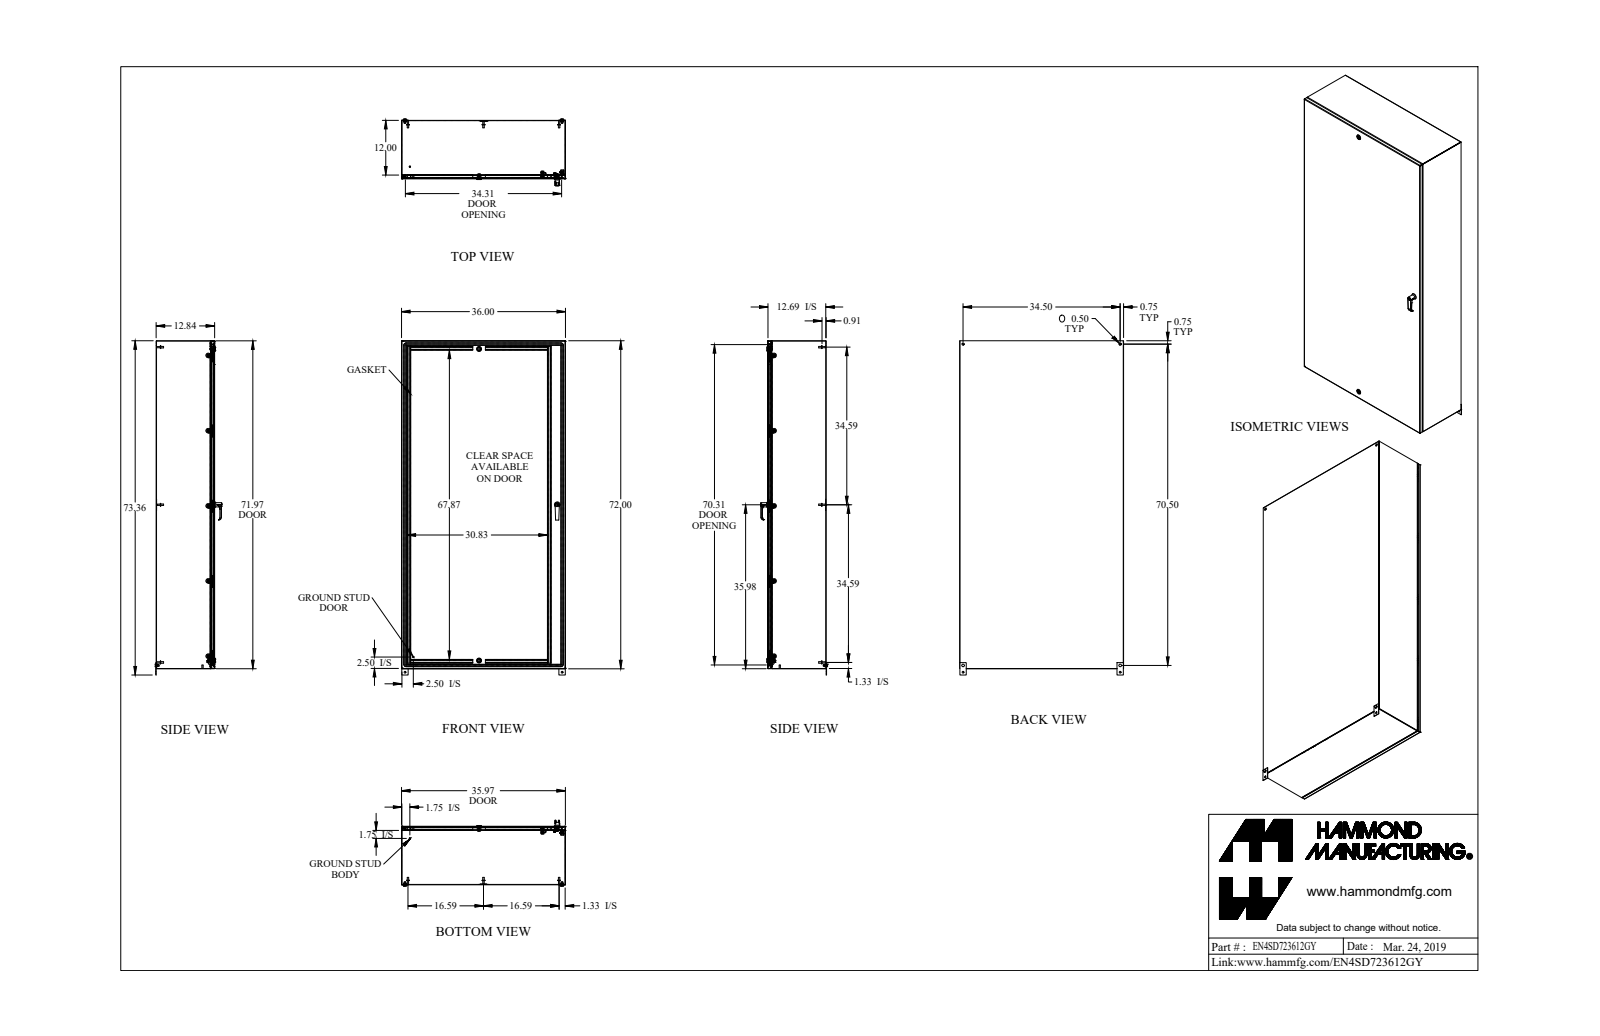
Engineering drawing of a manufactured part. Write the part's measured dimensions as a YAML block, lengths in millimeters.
part_name: "EN4SD723612GY"
step_written_by: "SolidWorks 2018 (AUTOMOTIVE_DESIGN)"
units: millimeters
bodies: {solids: 100, faces: 2461, planar: 1167, cylindrical: 902, other: 392}
overall_size: [1863.4, 914.4, 373.2]
volume: 10660000
surface_area: 11800000
round_holes:
  - {diameter: 4.5, count: 10}
  - {diameter: 5, count: 6}
  - {diameter: 6.4, count: 5}
  - {diameter: 6.7, count: 5}
  - {diameter: 10.5, count: 5}
  - {diameter: 6.5, count: 4}
  - {diameter: 8, count: 4}
  - {diameter: 9.9, count: 4}
  - {diameter: 10, count: 4}
  - {diameter: 12.7, count: 4}
  - {diameter: 5.9, count: 2}
  - {diameter: 7.8, count: 2}
round_bosses_or_shafts:
  - {diameter: 6.4, count: 11}
  - {diameter: 9.5, count: 10}
  - {diameter: 4, count: 10}
  - {diameter: 15.9, count: 9}
  - {diameter: 8, count: 8}
  - {diameter: 6.9, count: 8}
  - {diameter: 25.4, count: 5}
  - {diameter: 16, count: 4}
partial_cylinders:
  - {radius: 1.1, count: 24}
  - {radius: 1.6, count: 19}
  - {radius: 0.9, count: 17}
  - {radius: 2.7, count: 17}
  - {radius: 0.8, count: 15}
  - {radius: 3.2, count: 14}
  - {radius: 0.2, count: 10}
  - {radius: 2.4, count: 10}
face_to_face_distances: [1.8, 324.2, 322.4, 326.1, 912.6, 910.7, 914.4, 1827, 1825.1, 1828.8]
hole_center_spacings: [419.4, 876.3, 1257, 38.1, 63.7, 414.1, 418.8, 419.1]
